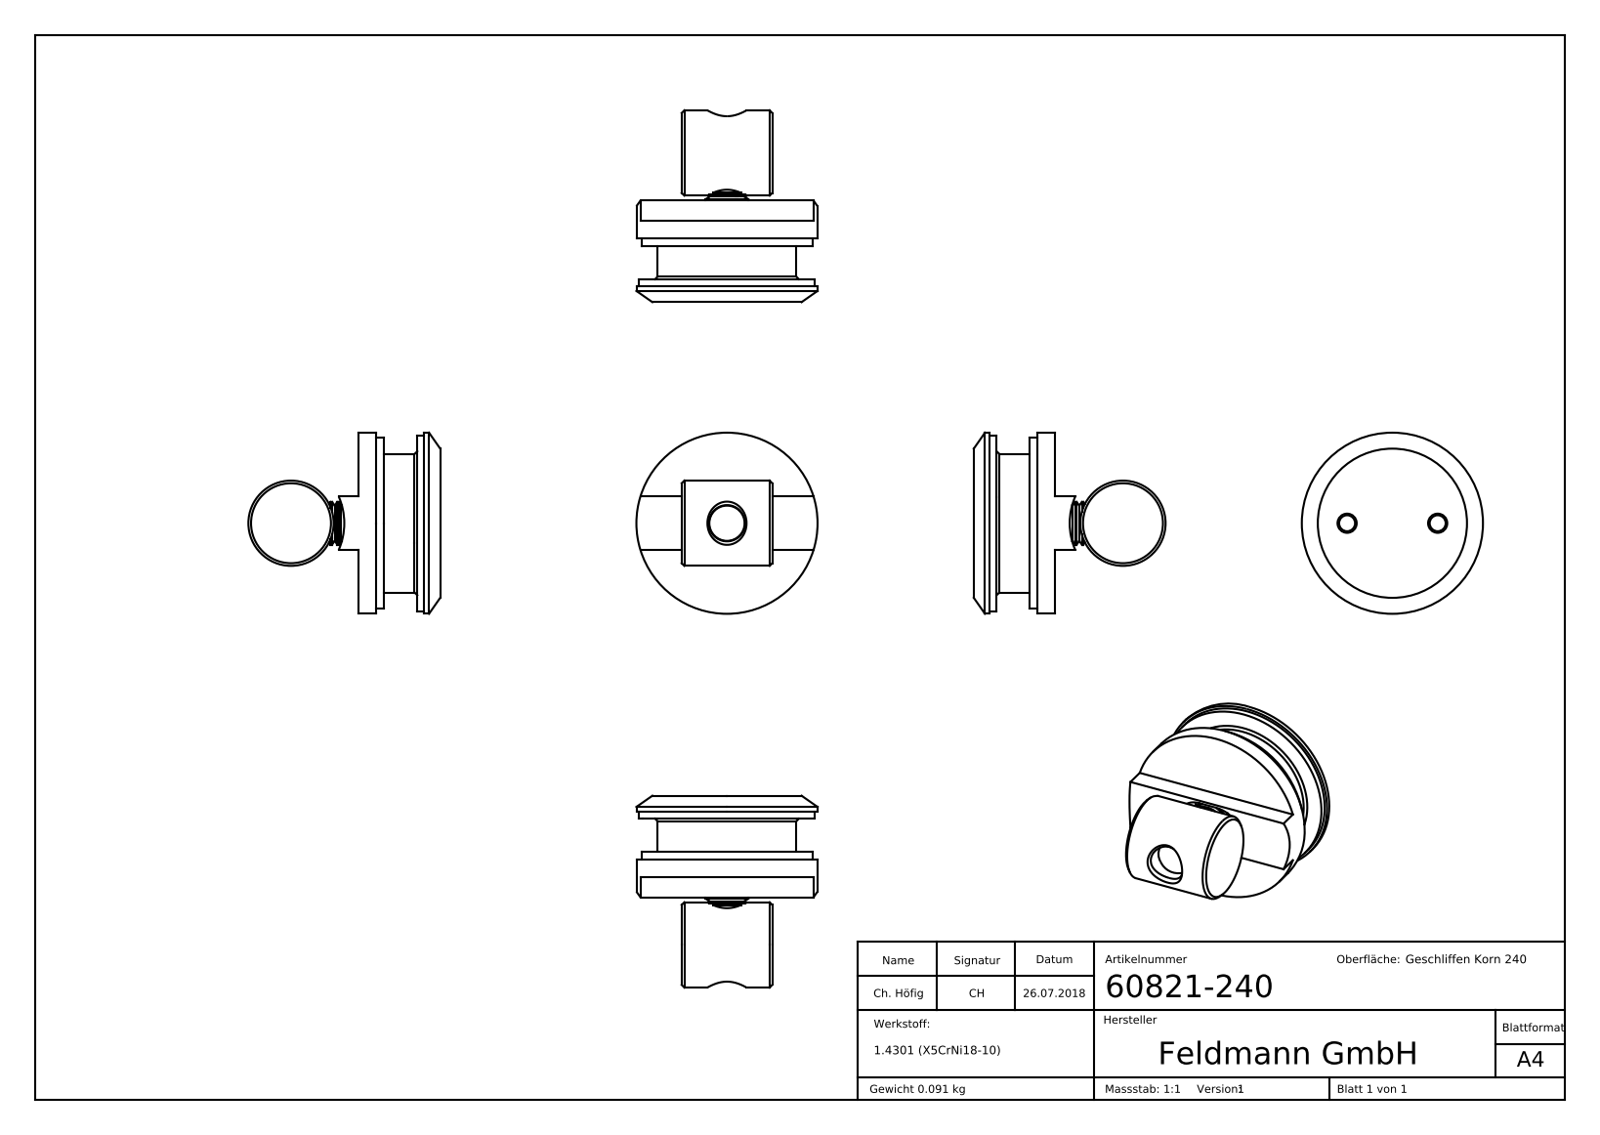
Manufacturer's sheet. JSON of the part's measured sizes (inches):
{"part_name": "60821-240; socket head cap screw_din_DIN 912 M8 x 20 --- 20S; 60821-240 Teil3_60821-240 Teil3; 60821-240 Teil5_60821-240 Teil5 (+3 more)", "step_written_by": "SolidWorks 2015 (CONFIG_CONTROL_DESIGN)", "units": "inches", "bodies": {"solids": 6, "faces": 416, "planar": 153, "cylindrical": 65, "other": 198}, "overall_size": [1.417, 1.339, 1.339], "volume_in3": 0.886, "surface_area_in2": 19.22, "round_holes": [[0.118, 2], [0.268, 1], [0.591, 1], [0.784, 1], [0.866, 1], [0.937, 1]], "round_bosses_or_shafts": [[1.339, 1], [1.299, 1], [1.26, 1], [1.024, 1], [0.929, 1], [0.846, 1], [0.63, 1], [0.512, 1]], "partial_cylinders_radius": [[0.167, 2], [0.492, 1]], "face_to_face_distances": [0.354, 0.118, 0.484, 0.472, 0.602, 0.13, 0.413, 0.295, 0.059, 0.189], "hole_center_spacings": [0.335, 0.669]}
